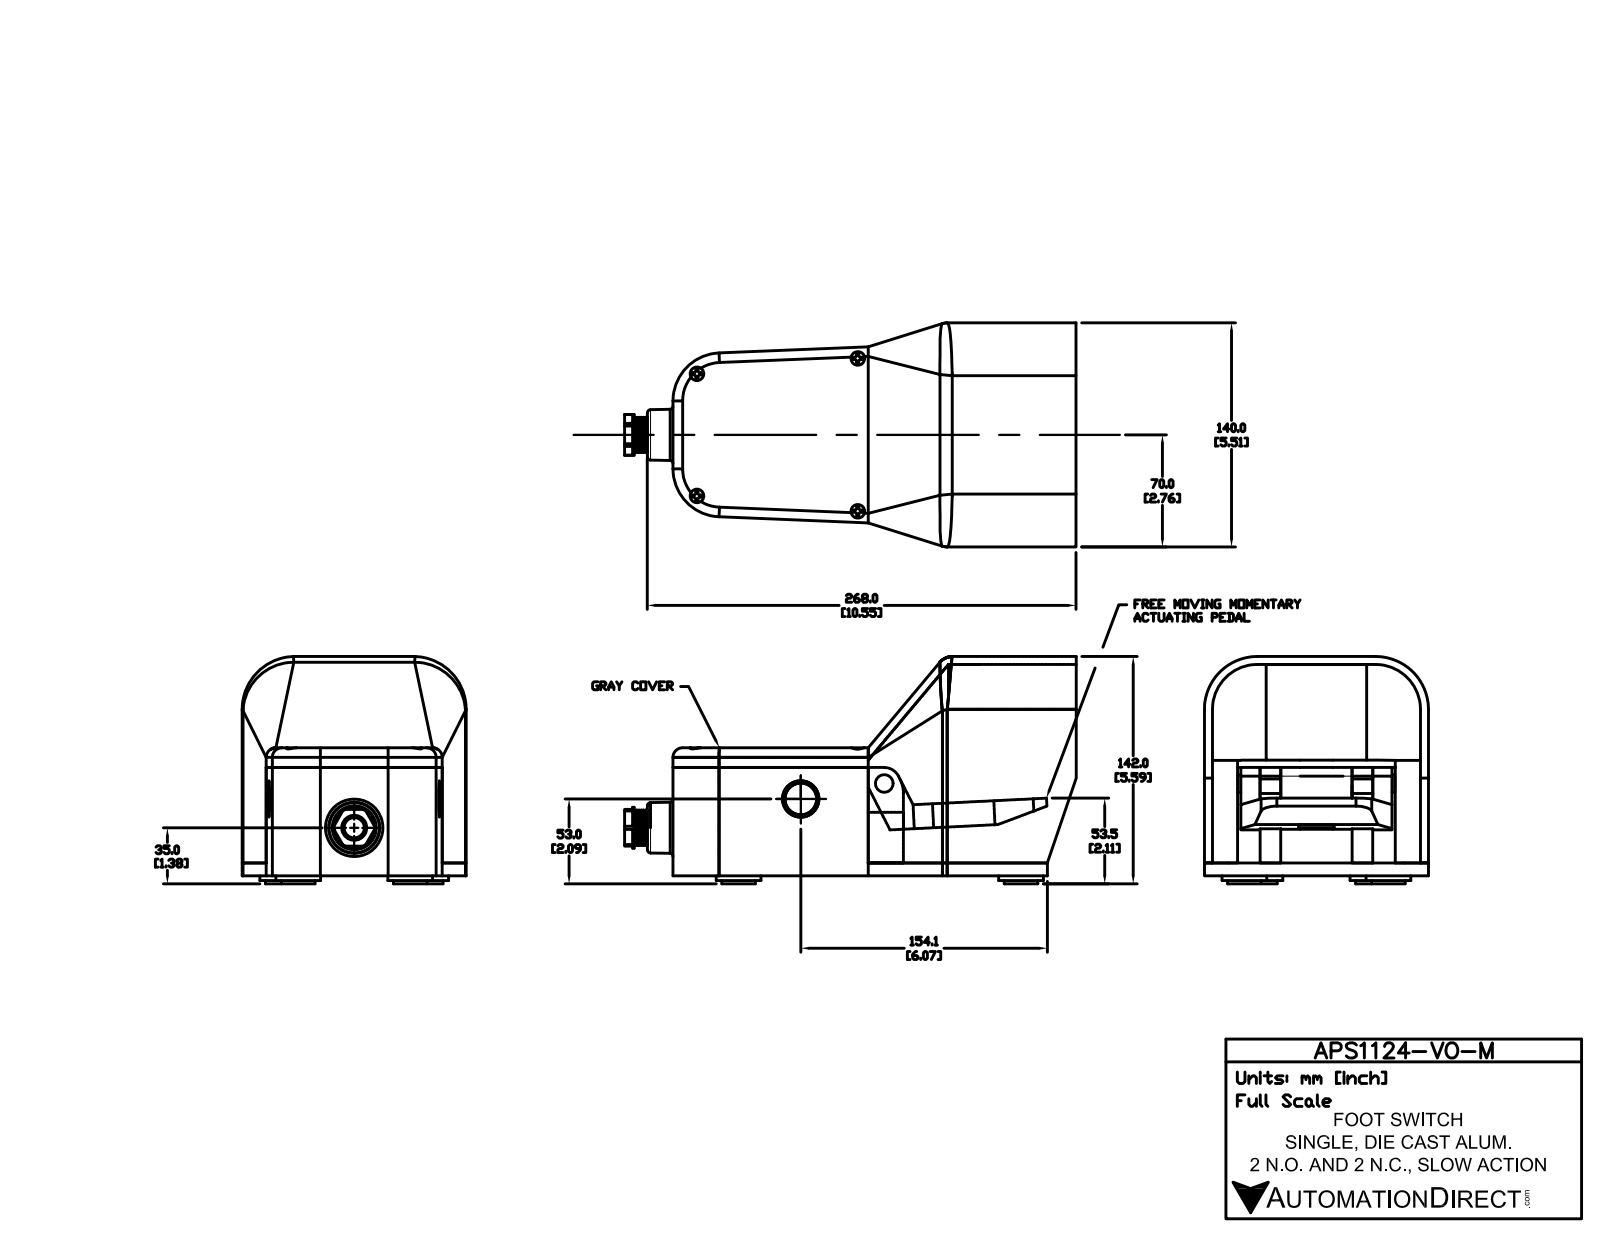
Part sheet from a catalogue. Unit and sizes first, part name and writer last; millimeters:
Units: millimetres
Overall size (bounding box): 282.25 × 142 × 140
Round holes (diameter × count): ⌀8.5 ×4, ⌀22.75 ×2, ⌀12.65 ×1, ⌀15.6 ×1
Round bosses / shafts (diameter × count): ⌀28 ×4, ⌀21 ×4, ⌀19.87 ×2, ⌀25.5 ×1, ⌀22 ×1, ⌀11 ×1
Partial cylindrical surfaces — rounded edges, fillets, slot ends (radius × count): R1 ×16, R10 ×6, R5.99 ×3, R28 ×2, R30 ×2, R33 ×2, R20 ×1
Main face-to-face distances: 5, 135, 8, 59.64, 67.67, 59.67, 67.64, 140, 80, 72
Hole centre spacings: 101, 132.24, 76.3, 95.5
Volume: 1 541 000 mm³ · Surface area: 267 977 mm²
Bodies: 18 solids, 361 faces (214 planar, 91 cylindrical, 56 other)
Part name (STEP PRODUCT): APS1124-V0-M
STEP written by: SolidWorks 2015 (AUTOMOTIVE_DESIGN)
